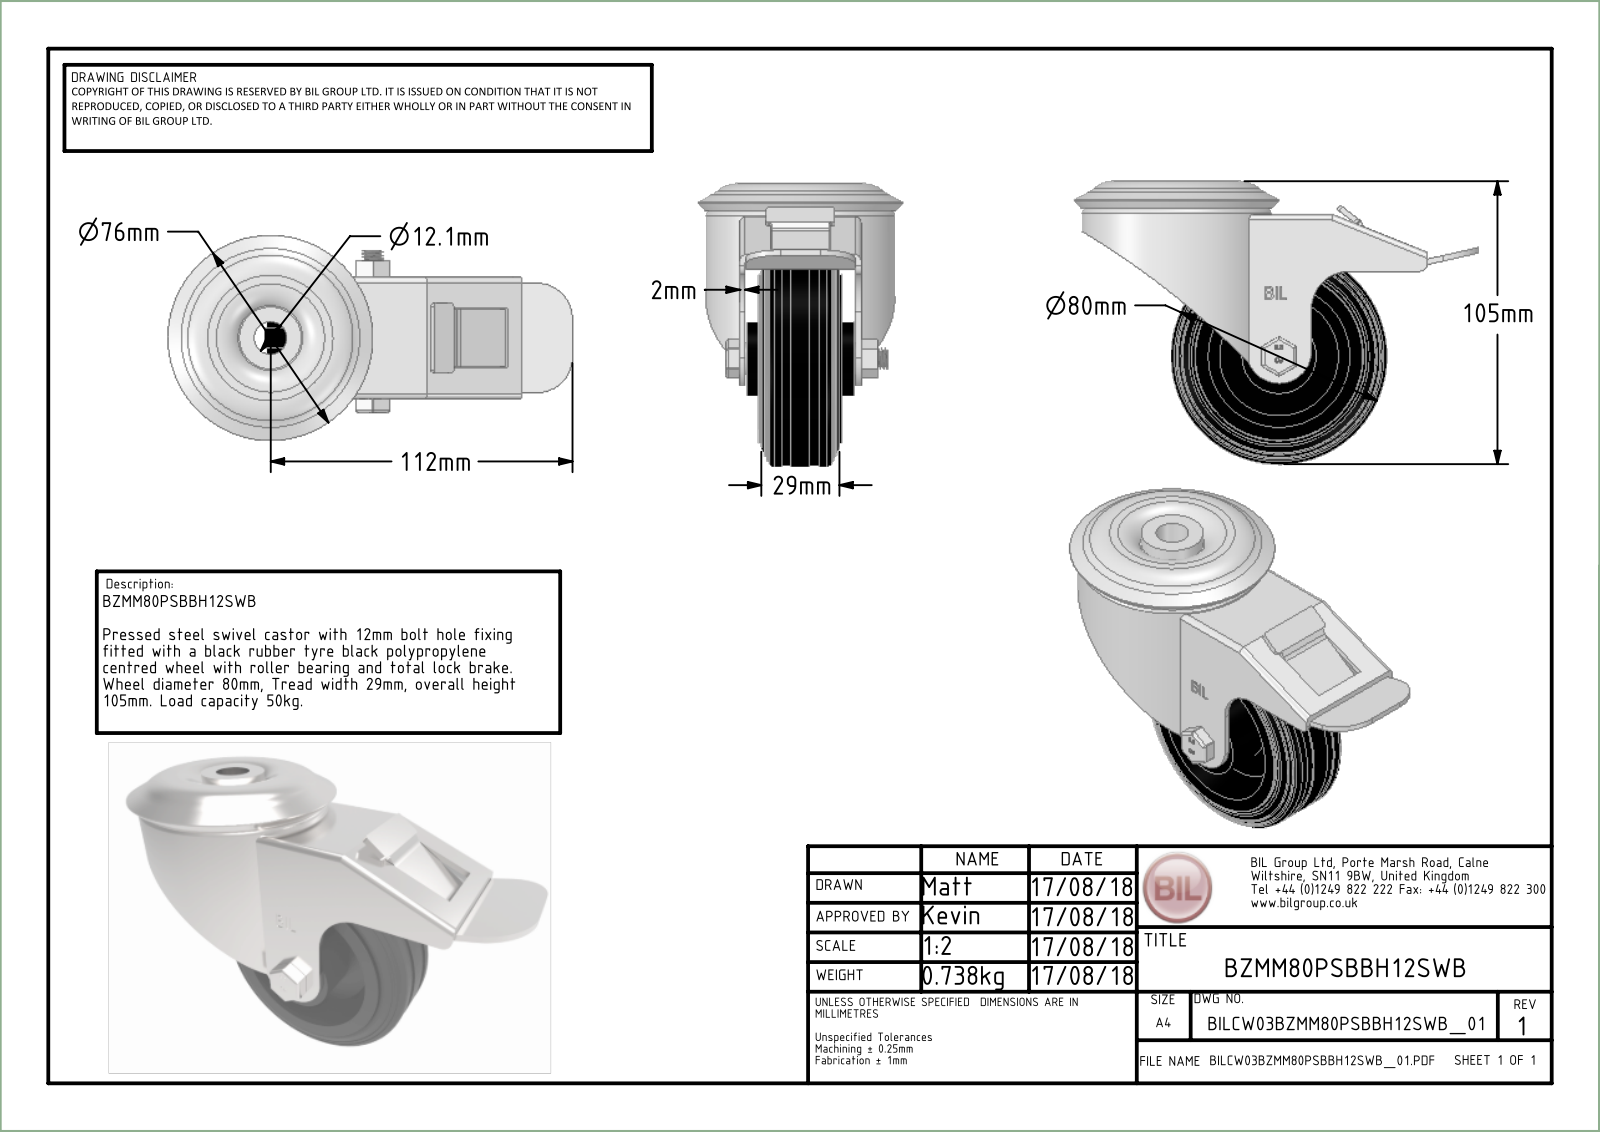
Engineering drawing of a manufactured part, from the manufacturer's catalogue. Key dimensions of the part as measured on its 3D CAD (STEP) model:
Part name (STEP PRODUCT): BZMM80PSBBH12SWB v3; BZMM80ASBH12SWB v1; ZINC PLATED, PRESSED STEEL HEAD; ZINC PLATED, PRESSED STEEL FORKS (+8 more)
STEP written by: Autodesk Translation Framework v13.20.0.188 (AP242_MANAGED_MODEL_BASED_3D_ENGINEERING_MIM_LF)
Units: millimetres
Bodies: 20 solids, 730 faces (348 planar, 248 cylindrical, 134 other)
Overall size (bounding box): 150 × 105 × 76
Volume: 183 540 mm³ · Surface area: 106 713 mm²
Round holes (diameter × count): ⌀0.66 ×2, ⌀12.2 ×2, ⌀8 ×1, ⌀8.2 ×1, ⌀8.4 ×1, ⌀8.6 ×1, ⌀12.5 ×1, ⌀20 ×1, ⌀25 ×1, ⌀48.32 ×1, ⌀51 ×1, ⌀55 ×1
Round bosses / shafts (diameter × count): ⌀3.75 ×8, ⌀70 ×1, ⌀61 ×1, ⌀49.5 ×1, ⌀38 ×1, ⌀24.9 ×1, ⌀24 ×1, ⌀21.31 ×1
Partial cylindrical surfaces — rounded edges, fillets, slot ends (radius × count): R0.75 ×48, R0.5 ×26, R0.25 ×12, R1 ×6, R1.25 ×6, R2 ×5, R2.5 ×5, R0.33 ×4
Main face-to-face distances: 2.5, 5.5, 8, 42.5, 17.25, 37, 34.5, 40, 25.25, 4.5
Hole centre spacings: 3.22, 2.49
